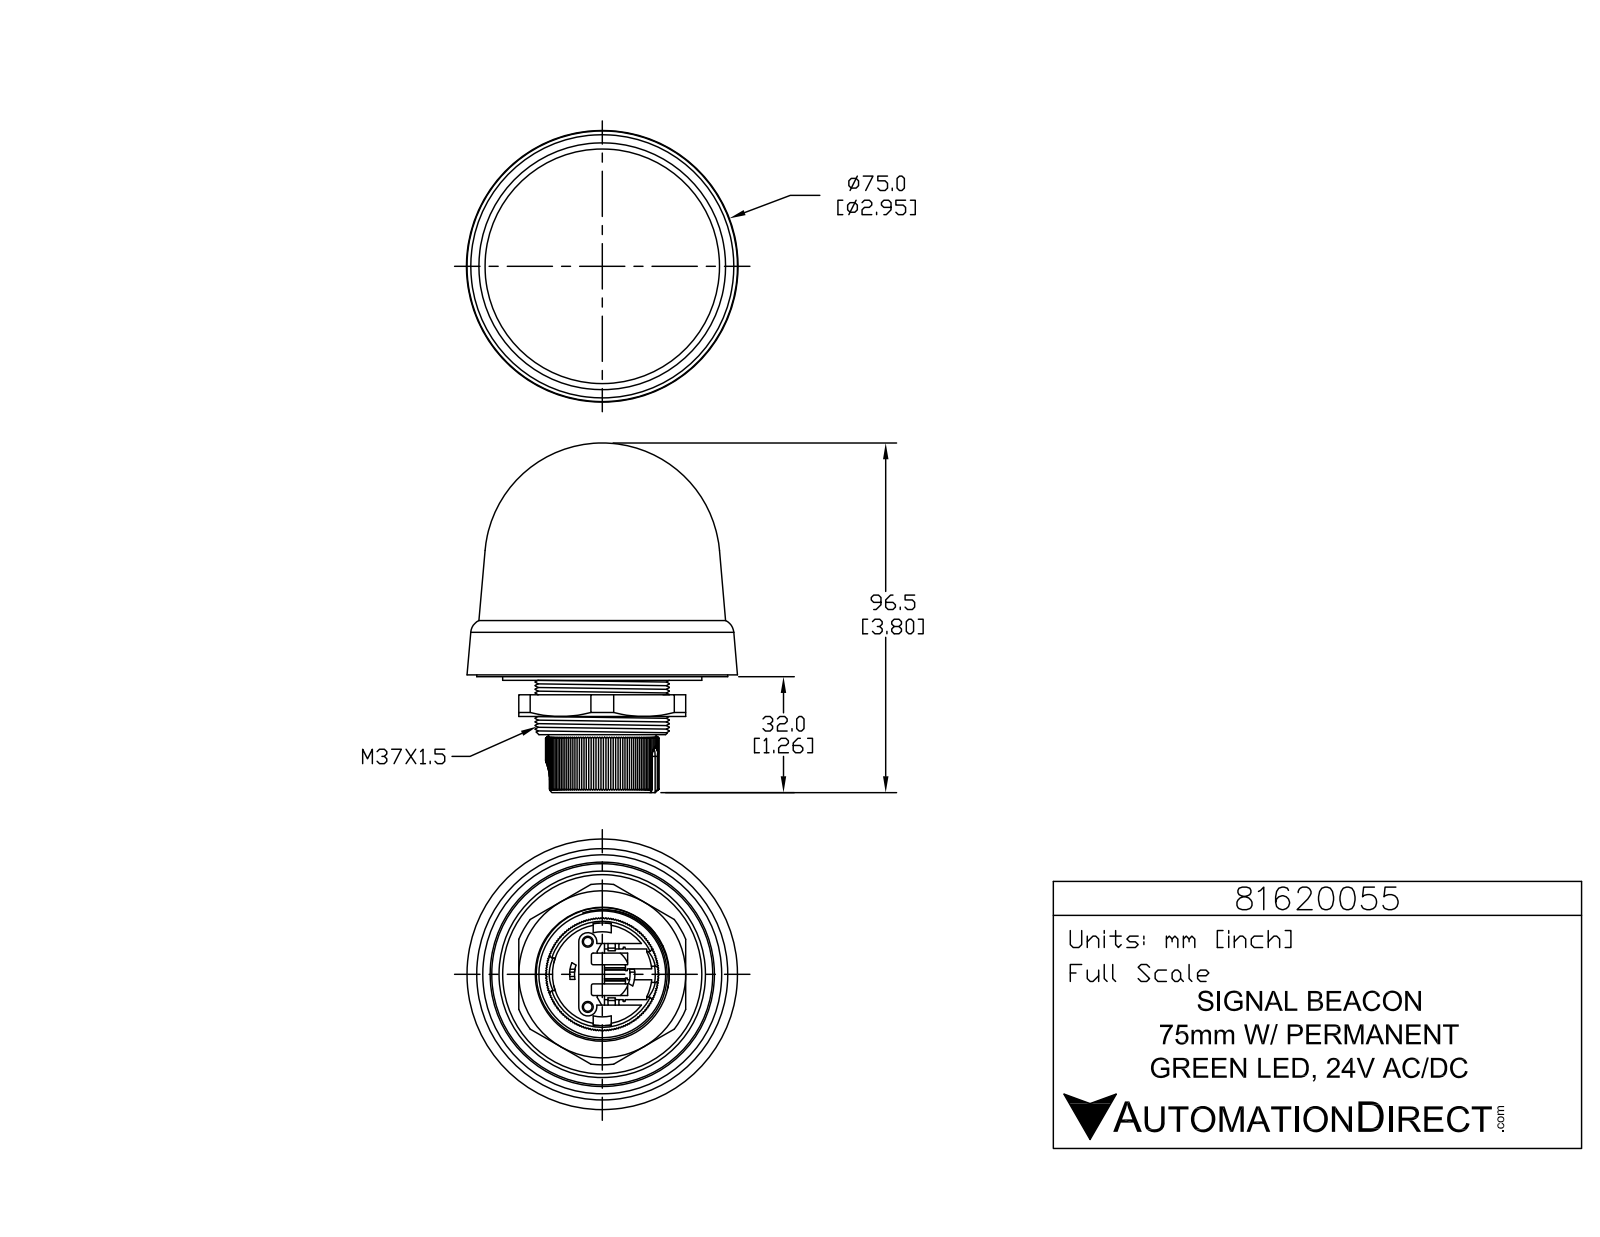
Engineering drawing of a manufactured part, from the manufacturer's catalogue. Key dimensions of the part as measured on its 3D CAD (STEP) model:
Part name (STEP PRODUCT): 81620055
STEP written by: SolidWorks 2019 (CONFIG_CONTROL_DESIGN)
Units: inches
Bodies: 3 solids, 560 faces (432 planar, 80 cylindrical, 48 other)
Overall size (bounding box): 3.799 × 2.941 × 2.941
Volume: 12.36 in³ · Surface area: 58.68 in²
Round holes (diameter × count): ⌀0.094 ×2, ⌀0.118 ×2, ⌀0.604 ×1, ⌀1.142 ×1
Round bosses / shafts (diameter × count): ⌀0.217 ×2, ⌀0.067 ×2, ⌀2.165 ×1, ⌀1.457 ×1, ⌀0.925 ×1
Partial cylindrical surfaces — rounded edges, fillets, slot ends (radius × count): R0.008 ×6, R0.039 ×6, R0.02 ×4, R0.031 ×2, R0.079 ×2, R0.098 ×2, R0.177 ×1, R0.354 ×1
Main face-to-face distances: 0.177, 0.354, 0.197, 0.433, 0.512, 0.335, 0.059, 0.394, 0.118, 0.157
Hole centre spacings: 0.388, 0.709
